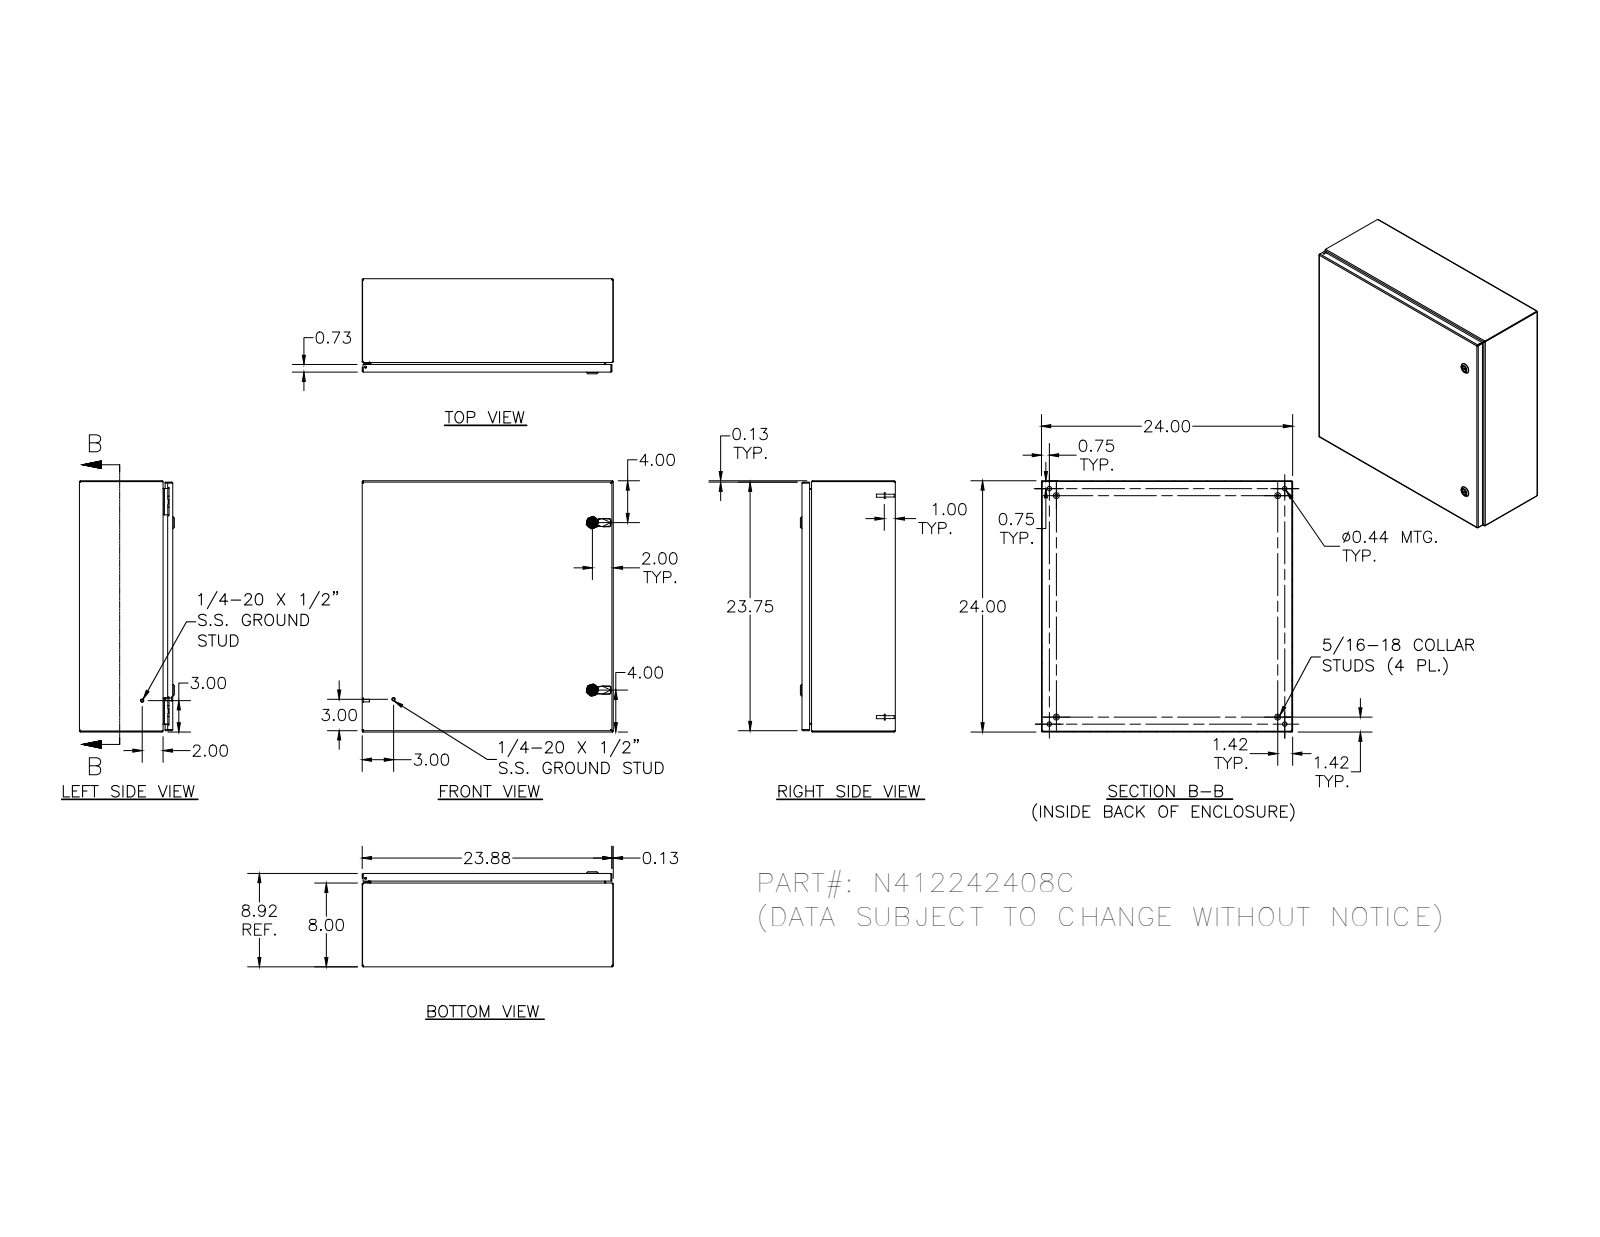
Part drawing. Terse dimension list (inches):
name: N412242408C
written by: SolidWorks 2018 (AUTOMOTIVE_DESIGN)
unit: in
bodies: 40 solids, 1812 faces (704 planar, 676 cylindrical, 432 other)
size: 24 × 24 × 9.075
volume: 157 in³; area: 4 258 in²
holes: 5× ⌀0.188, 4× ⌀0.093, 4× ⌀0.152, 4× ⌀0.167, 4× ⌀0.172, 4× ⌀0.437, 2× ⌀0.156, 2× ⌀0.197, 2× ⌀0.315, 2× ⌀0.394, 2× ⌀0.402, 2× ⌀0.634
bosses: 10× ⌀0.25, 4× ⌀0.563, 4× ⌀0.36, 4× ⌀0.32, 4× ⌀0.3, 4× ⌀0.256, 4× ⌀0.164, 4× ⌀0.131
rounds: 54× R0.012, 30× R0.031, 26× R0.05, 23× R0.02, 20× R0.105, 18× R0.016, 16× R0.125, 8× R0.032
face distances: 0.074, 8.843, 8.769, 8.917, 0.074, 23.926, 23.926, 24, 23.852, 0.917
hole spacings: 20, 0.66, 0.656, 1.307, 1.965, 19.34, 20.66, 1.619
